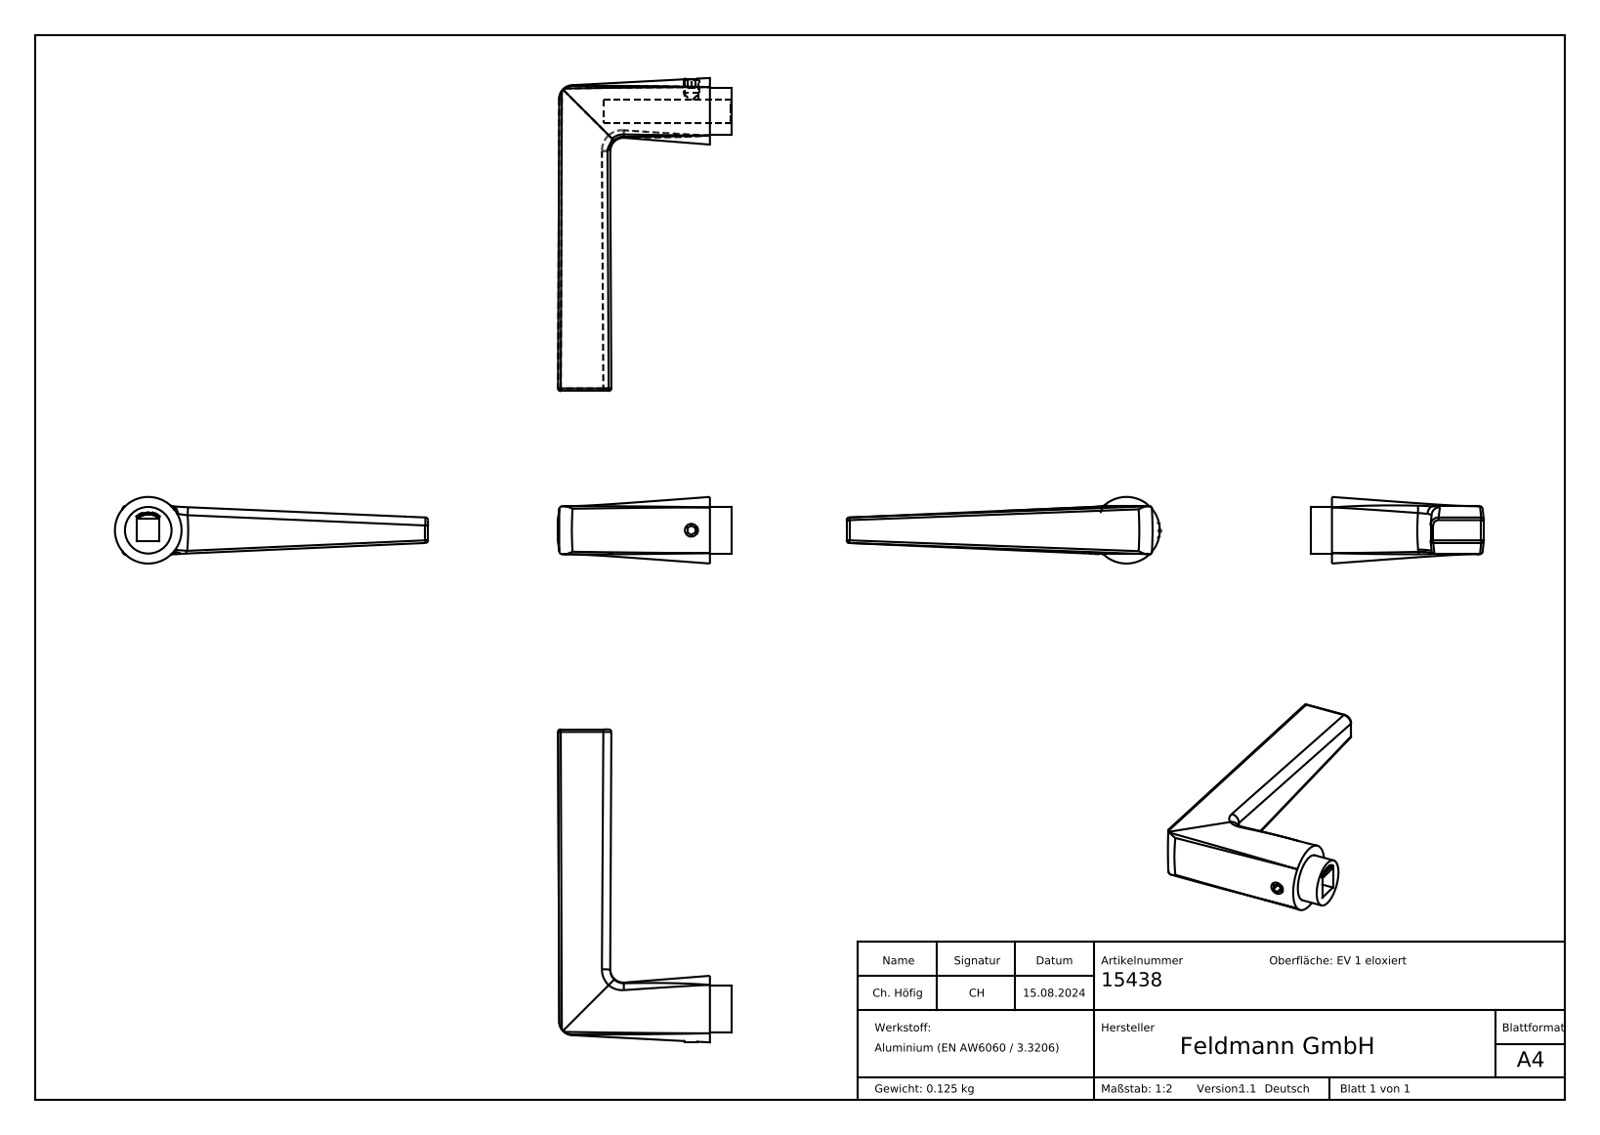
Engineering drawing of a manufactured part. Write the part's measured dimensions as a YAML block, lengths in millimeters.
part_name: "15438"
step_written_by: "SolidWorks 2015 (CONFIG_CONTROL_DESIGN)"
units: millimeters
bodies: {solids: 1, faces: 231, planar: 111, cylindrical: 7, other: 113}
overall_size: [117.5, 65, 25]
volume: 44678
surface_area: 13508
round_holes:
  - {diameter: 5, count: 1}
round_bosses_or_shafts:
  - {diameter: 17.5, count: 1}
partial_cylinders:
  - {radius: 1, count: 2}
face_to_face_distances: [8.5, 8, 109.25, 100.75, 63, 55, 0.5, 7.5, 62.5, 0.32]
